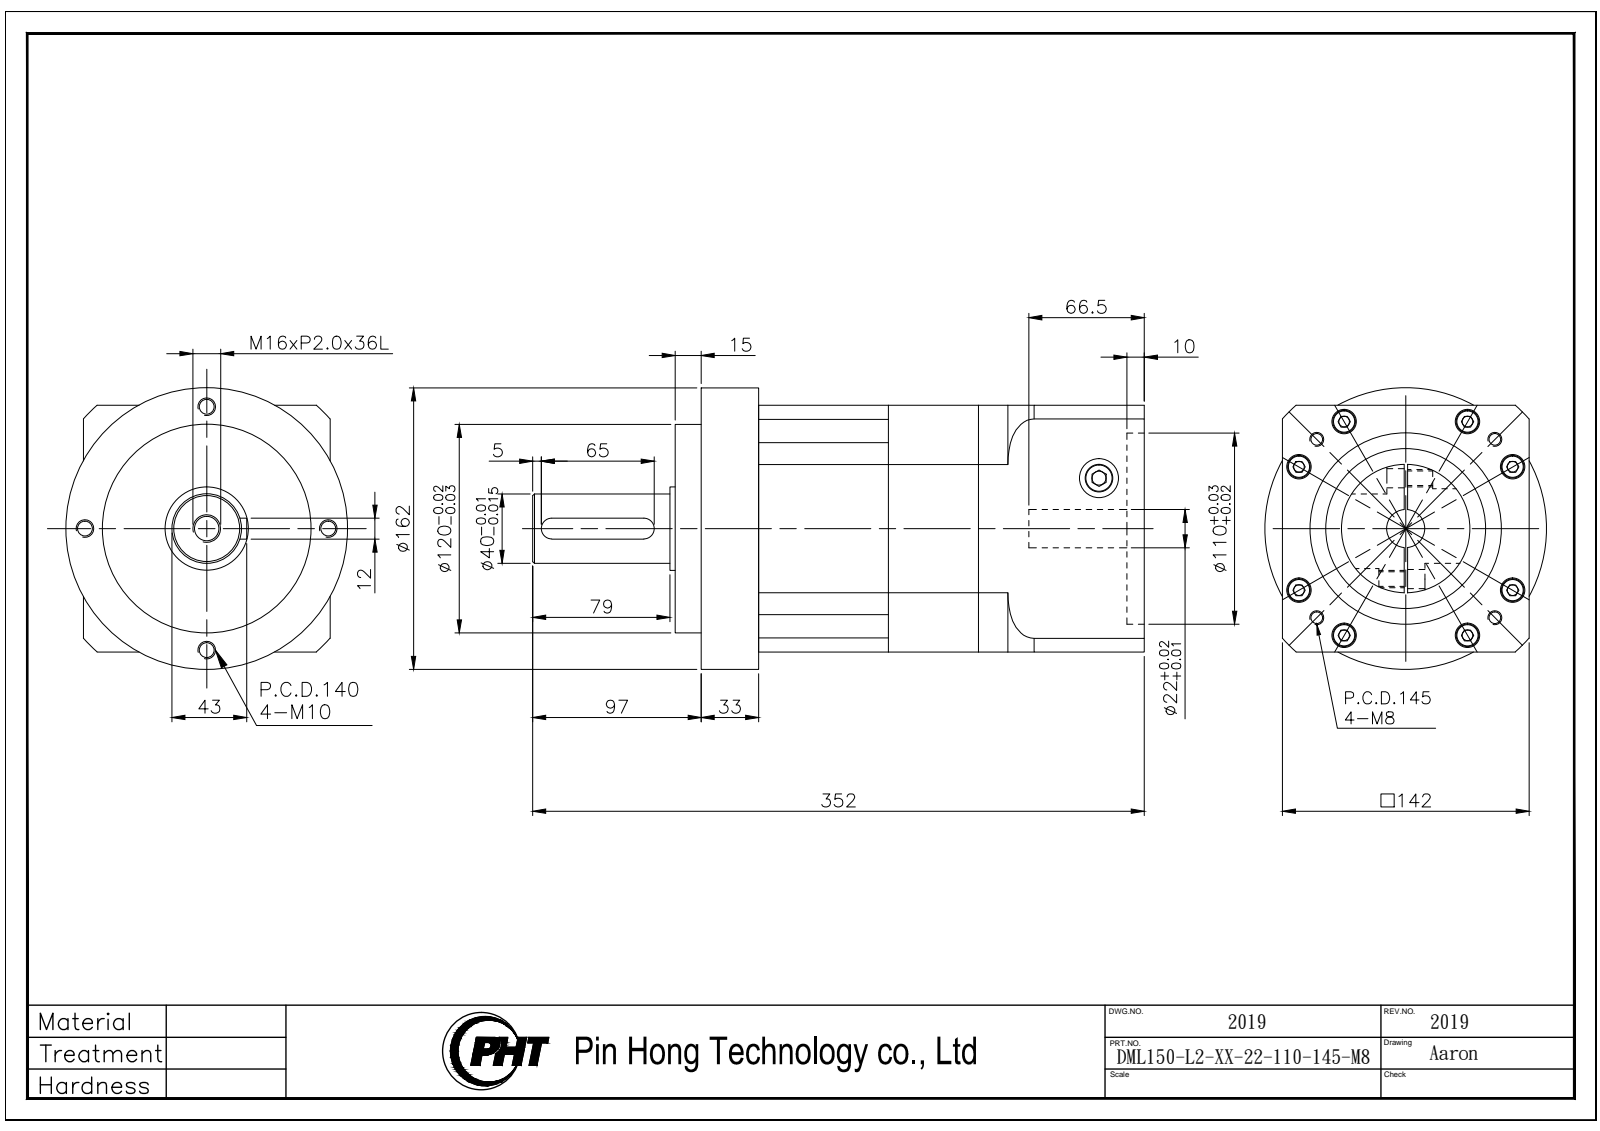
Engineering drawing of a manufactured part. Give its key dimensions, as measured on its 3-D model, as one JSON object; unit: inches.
{"part_name": "DML150-L2-XX-22-110-145-M8_2019", "step_written_by": "SolidWorks 2016 (AUTOMOTIVE_DESIGN)", "units": "inches", "bodies": {"solids": 4, "faces": 273, "planar": 114, "cylindrical": 119, "other": 40}, "overall_size": [13.858, 6.378, 6.378], "volume_in3": 289.7, "surface_area_in2": 592.8, "round_holes": [[0.551, 9], [0.354, 8], [0.268, 4], [0.335, 4], [0.886, 2], [0.866, 1], [3.622, 1], [4.331, 1]], "round_bosses_or_shafts": [[0.512, 8], [6.378, 1], [4.724, 1], [2.913, 1], [1.89, 1], [1.575, 1]], "partial_cylinders_radius": [[0.394, 4], [0.236, 2], [3.15, 1], [3.74, 1]], "face_to_face_distances": [5.591, 2.941, 2.039, 4.98, 1.89, 6.87, 4.831, 3.76, 5.799, 8.74], "hole_center_spacings": [2.795, 0.74, 1.437, 2.149, 2.776, 3.44, 3.953, 4.483]}
